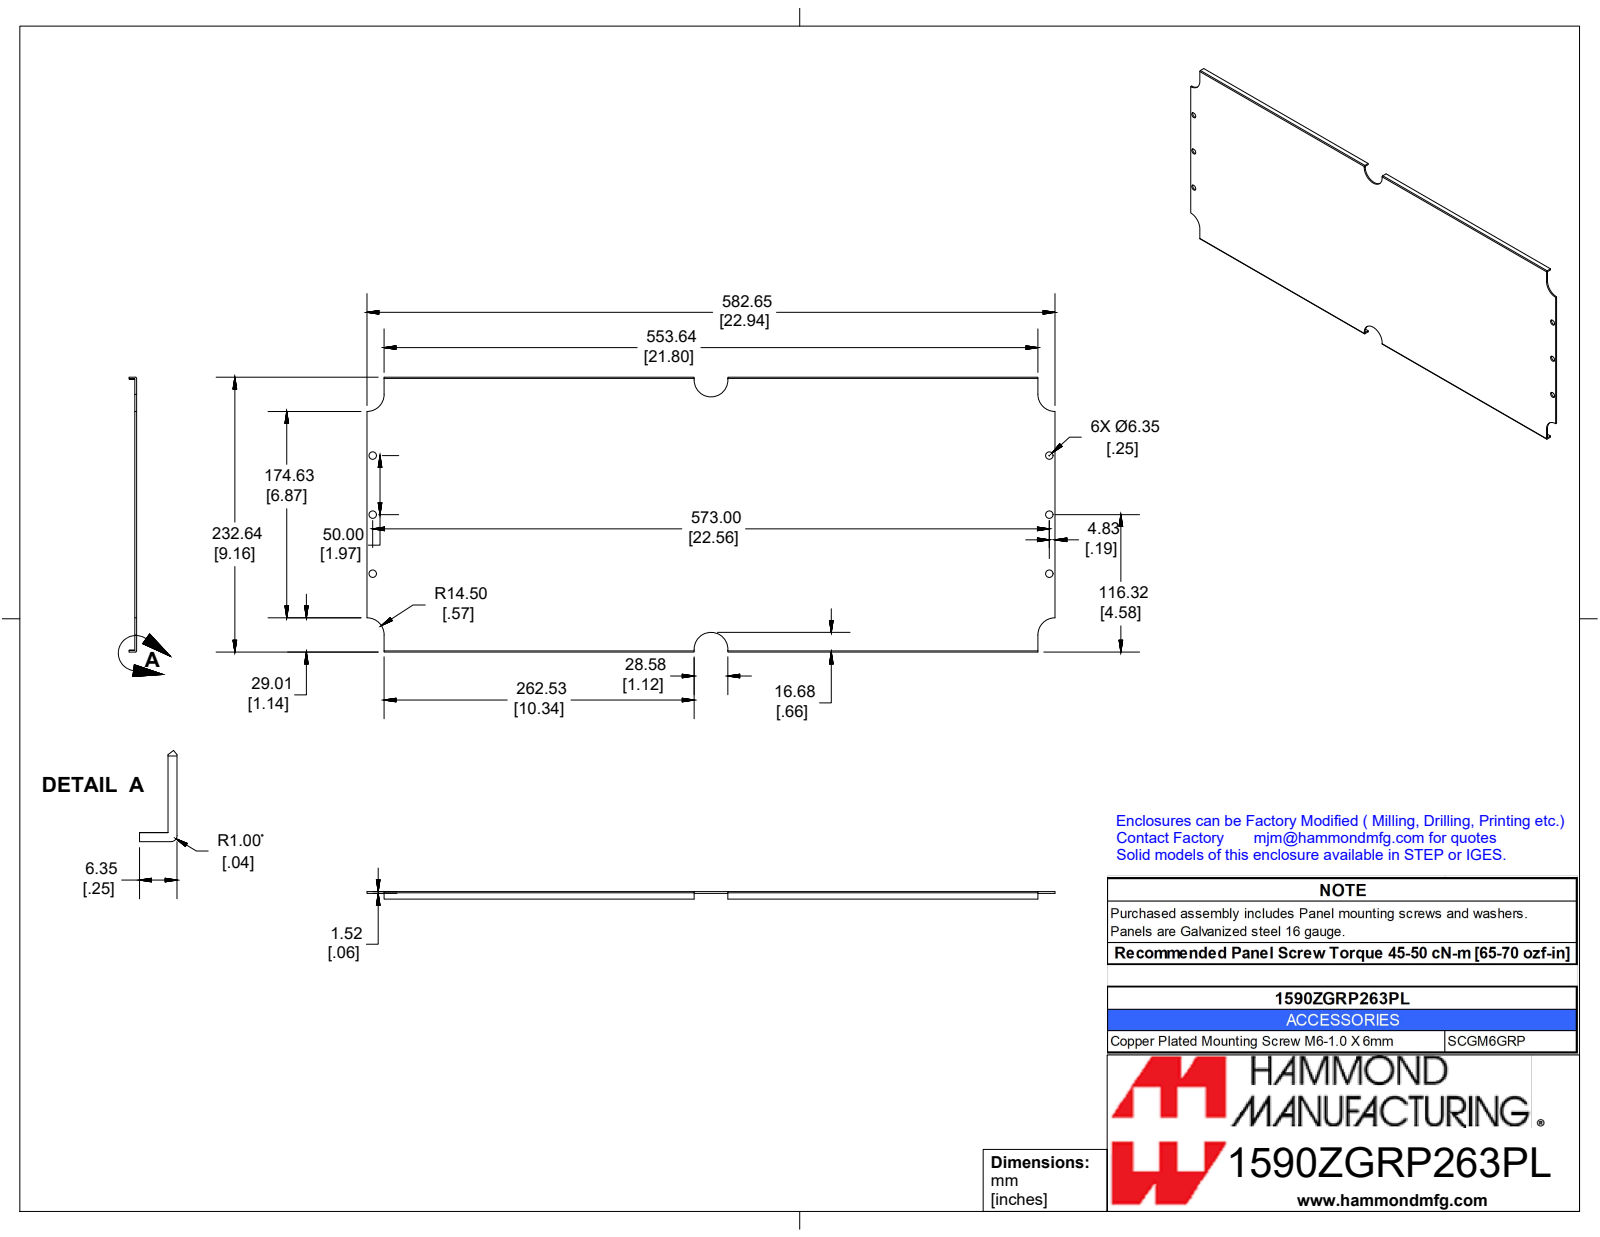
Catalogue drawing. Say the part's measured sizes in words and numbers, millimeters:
The part is named "1590ZGRP263PL". Its 3-D file was written by "SolidWorks 2019 (CONFIG_CONTROL_DESIGN)". It is 1 solid with 40 faces: 24 planar, 16 cylindrical and 0 other. Overall it measures 582.7 by 232.6 by 6.4 millimeters. Its volume is 210 400 cubic millimeters and its surface area 278 600 square millimeters. Round holes: 6 of diameter 6.4. Partial cylindrical surfaces (rounded edges, fillets, slot ends): 4 of radius 14.5, 2 of radius 1, 2 of radius 14.3. The main face-to-face distances are 1.5, 232.6, 231.1, 1.5, 231.1, 229.6, 4.8, 6.4, 229.6, 229.6. The hole center spacings are 50, 575.2, 573, 100, 581.7.
